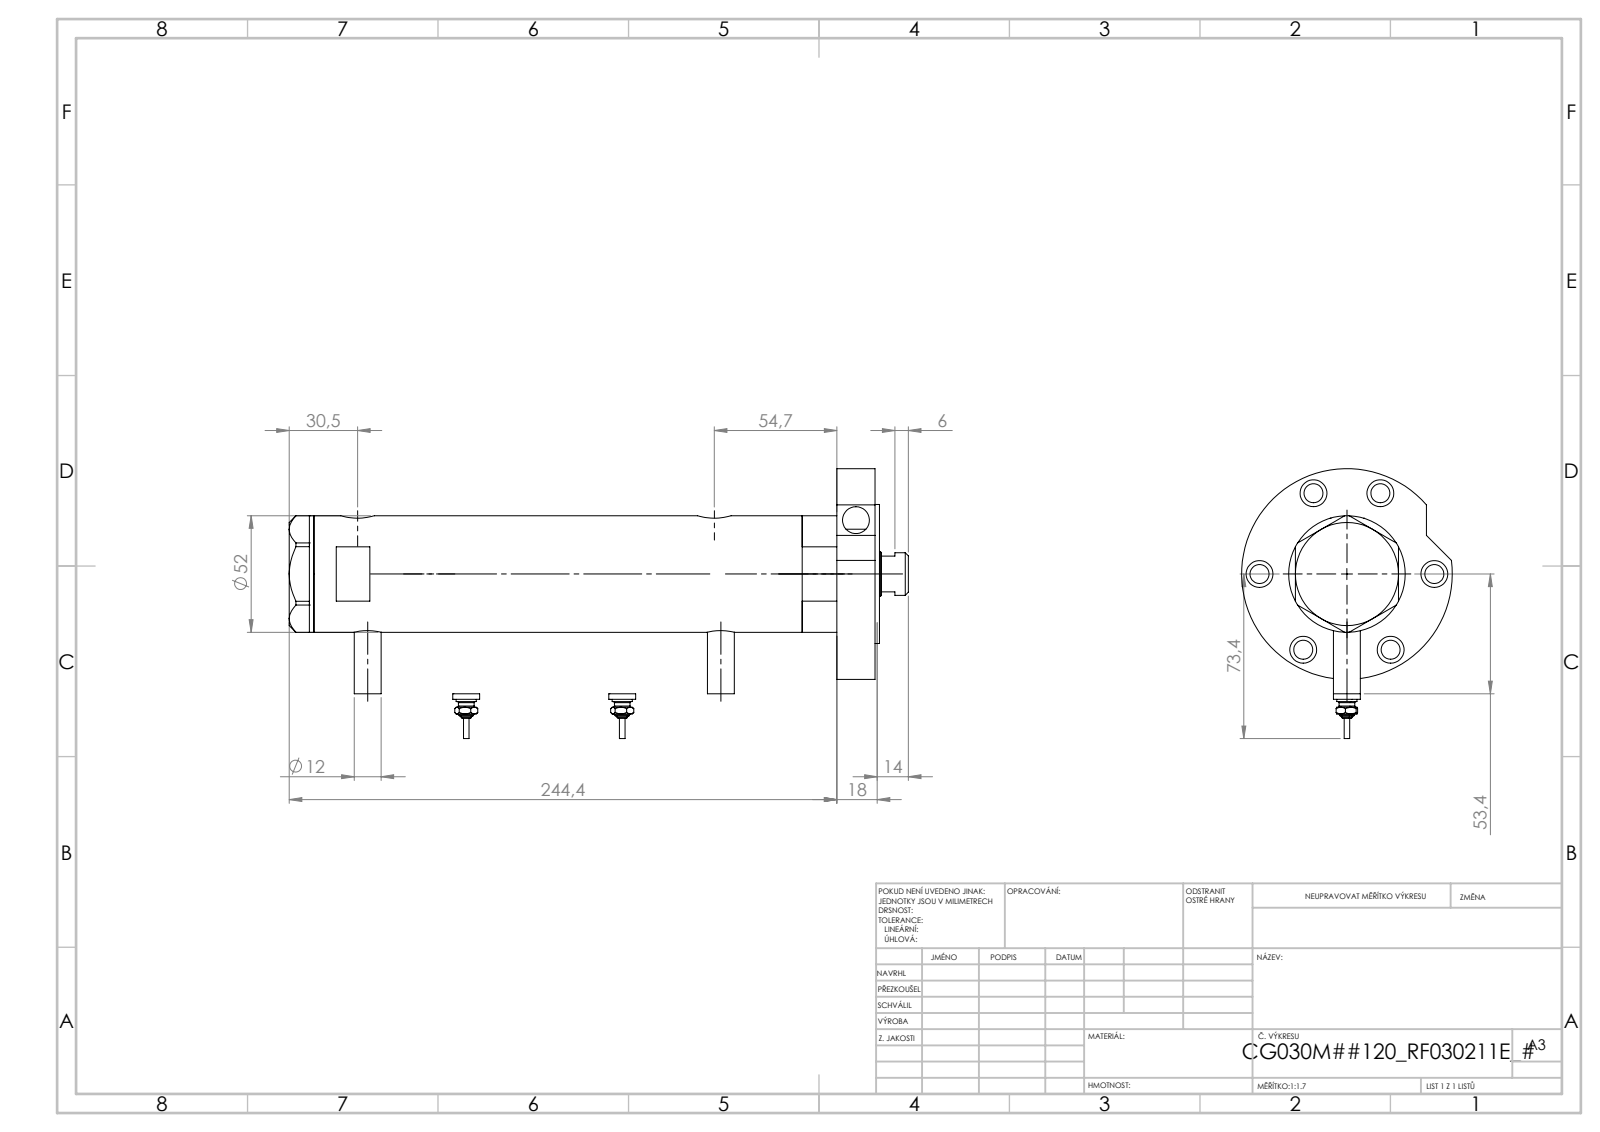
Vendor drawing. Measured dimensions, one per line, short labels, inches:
name: V270CG_MIDDLE; V270CG_FRONT; V270CG_VC; V270CG_SWITCH (+2 more)
written by: SolidWorks 2019 (CONFIG_CONTROL_DESIGN)
unit: in
bodies: 7 solids, 290 faces (106 planar, 110 cylindrical, 74 other)
size: 10.591 × 4.146 × 3.701
volume: 34.17 in³; area: 200.4 in²
holes: 7× ⌀0.472, 6× ⌀0.335, 2× ⌀0.197, 2× ⌀0.383, 2× ⌀0.492, 2× ⌀0.591, 1× ⌀0.256, 1× ⌀0.787, 1× ⌀0.846, 1× ⌀1.181, 1× ⌀1.299, 1× ⌀1.575
bosses: 3× ⌀0.472, 2× ⌀0.354, 2× ⌀0.276, 2× ⌀0.171, 2× ⌀0.094, 1× ⌀3.701, 1× ⌀2.441, 1× ⌀2.047
face distances: 0.669, 8.876, 9.545, 0.079, 9.624, 0.748, 0.937, 7.939, 8.608, 8.687
hole spacings: 1.535, 0.114, 0.177, 1.706, 2.553, 2.659, 2.754, 3.064
